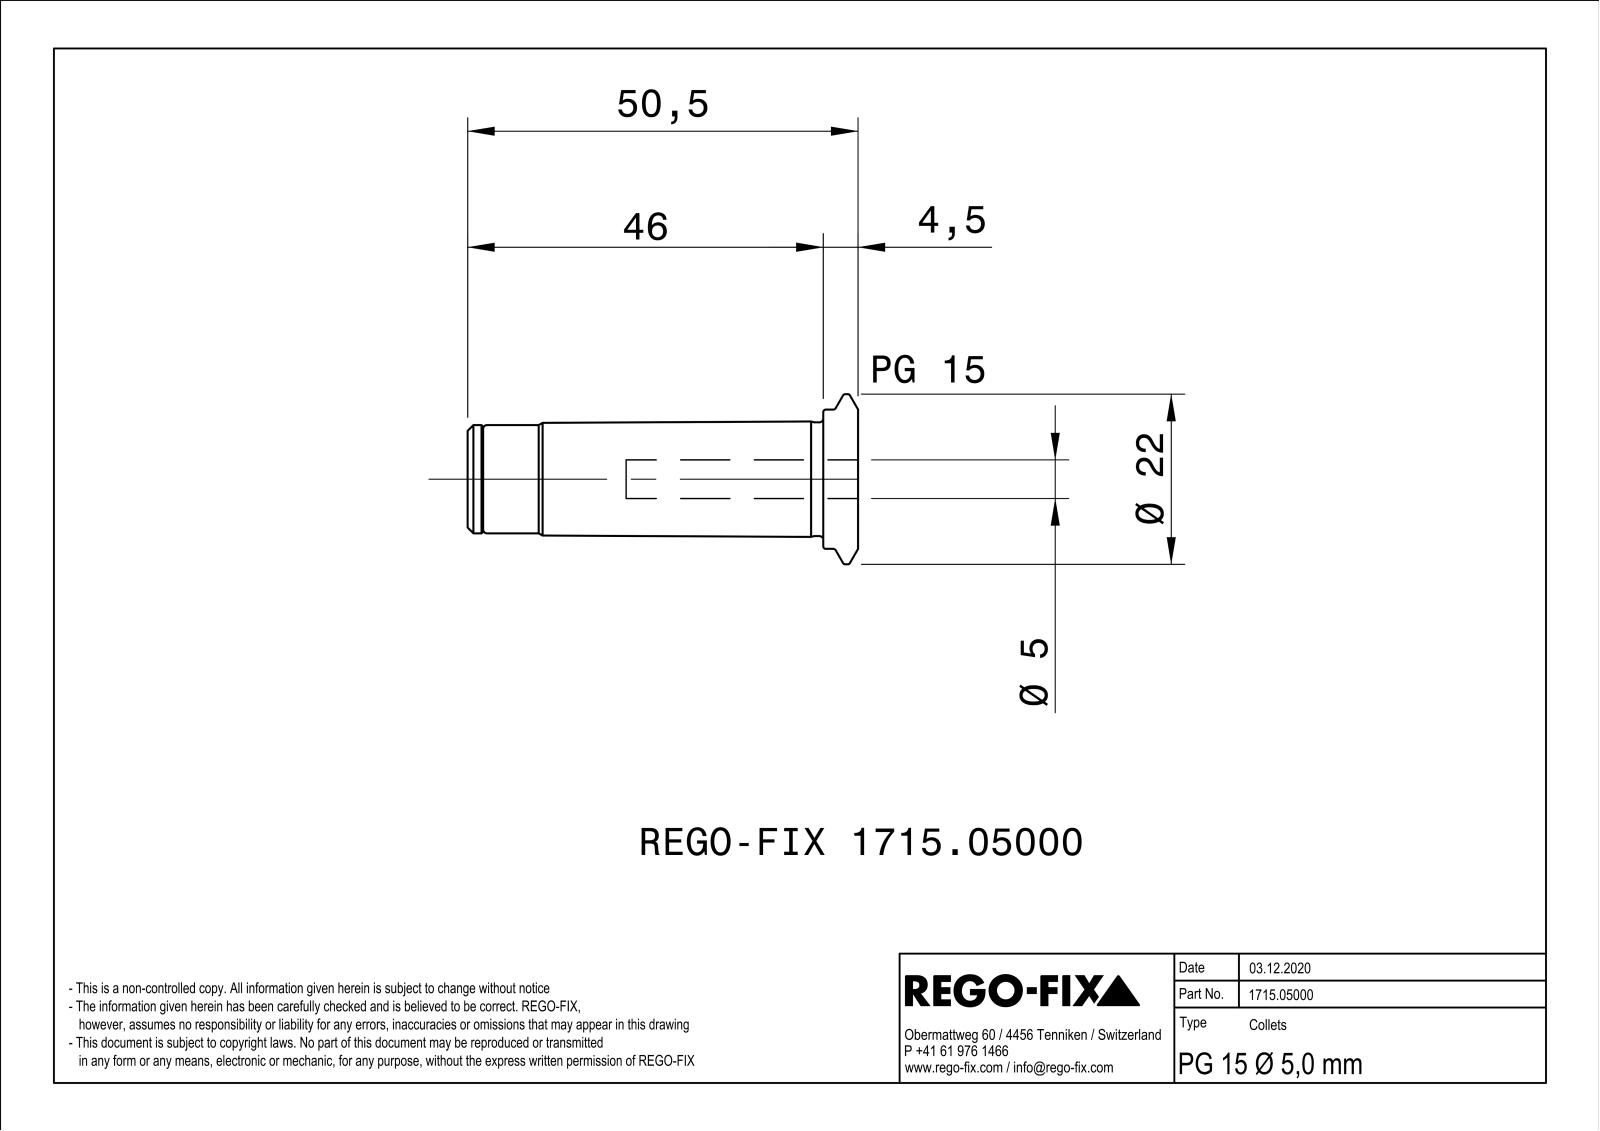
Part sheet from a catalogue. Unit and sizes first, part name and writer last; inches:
Units: inches
Overall size (bounding box): 1.988 × 0.866 × 0.866
Round holes (diameter × count): ⌀0.197 ×1, ⌀0.205 ×1, ⌀0.272 ×1, ⌀0.323 ×1, ⌀0.335 ×1, ⌀0.43 ×1, ⌀0.48 ×1
Round bosses / shafts (diameter × count): ⌀0.866 ×1, ⌀0.709 ×1, ⌀0.579 ×1, ⌀0.551 ×1
Partial cylindrical surfaces — rounded edges, fillets, slot ends (radius × count): R0.02 ×6, R0.205 ×1, R0.236 ×1
Main face-to-face distances: 0.039, 0.079, 1.988, 1.594, 0.394, 1.634, 0.354, 0.118, 0.177, 1.417
Bodies: 0 solids, 117 faces (35 planar, 32 cylindrical, 50 other)
Part name (STEP PRODUCT): NOCUT
STEP written by: SIEMENS PLM Software Solid Edge ST10 (AUTOMOTIVE_DESIGN)
